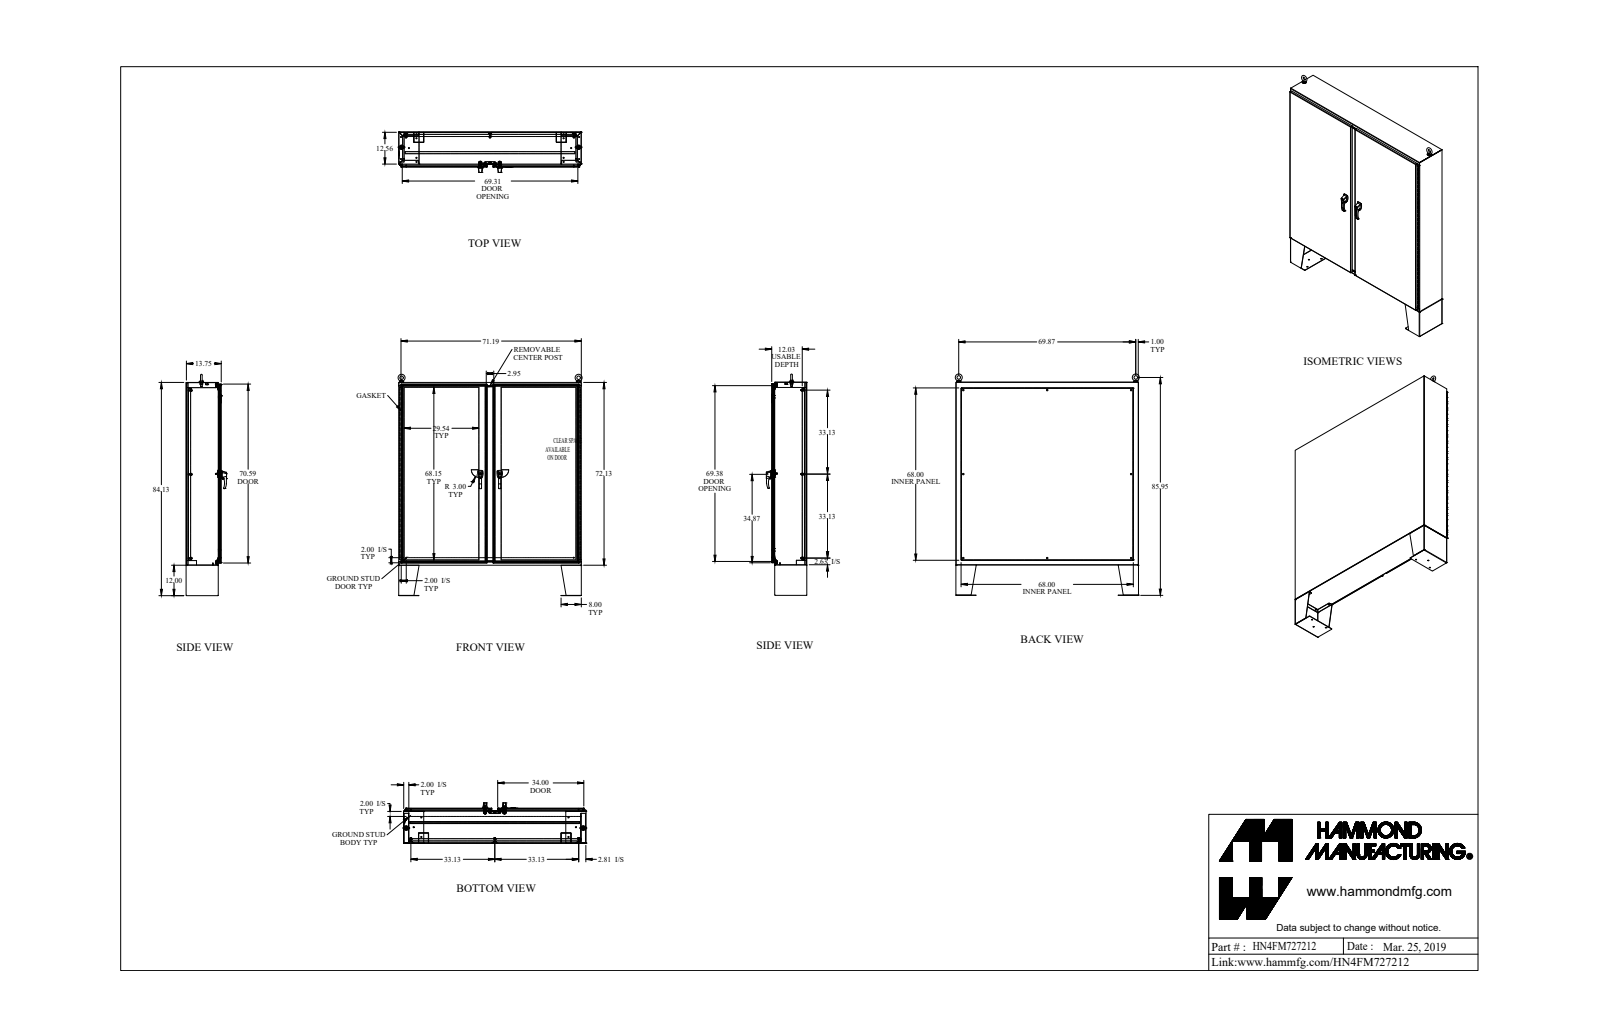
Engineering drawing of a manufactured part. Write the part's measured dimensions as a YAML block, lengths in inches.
part_name: "HN4FM727212"
step_written_by: "SolidWorks 2018 (AUTOMOTIVE_DESIGN)"
units: inches
bodies: {solids: 132, faces: 3996, planar: 1828, cylindrical: 1795, other: 373}
overall_size: [87.315, 72.607, 15.99]
volume: 2494
surface_area: 46619
round_holes:
  - {diameter: 0.304, count: 24}
  - {diameter: 0.437, count: 14}
  - {diameter: 0.307, count: 8}
  - {diameter: 0.35, count: 8}
  - {diameter: 0.563, count: 8}
  - {diameter: 0.25, count: 6}
  - {diameter: 0.445, count: 6}
  - {diameter: 0.281, count: 4}
  - {diameter: 0.313, count: 4}
  - {diameter: 0.39, count: 4}
  - {diameter: 0.201, count: 3}
  - {diameter: 0.313, count: 3}
round_bosses_or_shafts:
  - {diameter: 1, count: 10}
  - {diameter: 0.65, count: 8}
  - {diameter: 0.375, count: 8}
  - {diameter: 0.33, count: 8}
  - {diameter: 0.281, count: 8}
  - {diameter: 0.75, count: 4}
  - {diameter: 0.625, count: 4}
  - {diameter: 0.44, count: 4}
partial_cylinders:
  - {radius: 0.5, count: 33}
  - {radius: 0.018, count: 32}
  - {radius: 0.125, count: 32}
  - {radius: 0.06, count: 28}
  - {radius: 0.048, count: 27}
  - {radius: 0.143, count: 27}
  - {radius: 0.03, count: 12}
  - {radius: 0.09, count: 12}
face_to_face_distances: [0.125, 1.687, 0.095, 13.78, 13.655, 13.75, 13.875, 1.812, 11.968, 12.063]
hole_center_spacings: [6, 12, 18, 24, 74.07, 30, 36, 66.25]
